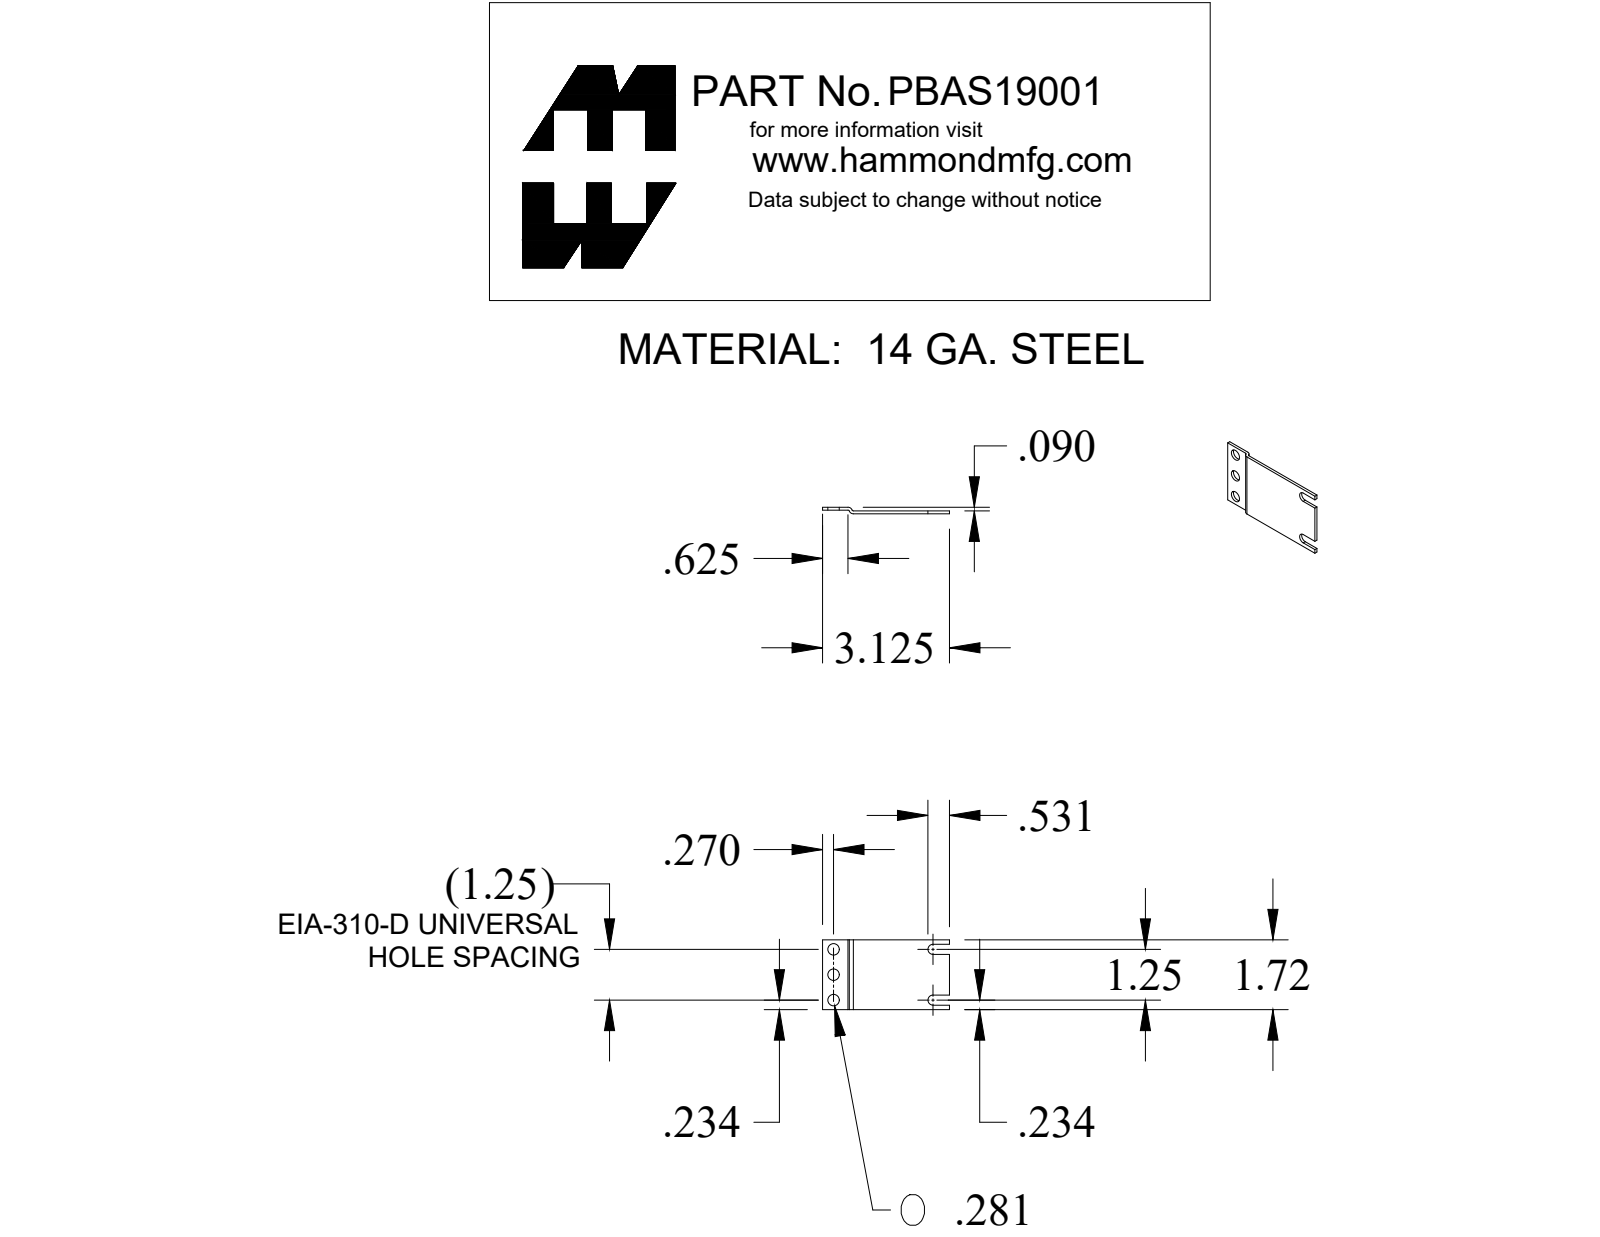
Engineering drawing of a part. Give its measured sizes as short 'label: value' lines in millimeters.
name: PBAS19001BK2
written by: SolidWorks 2019 (CONFIG_CONTROL_DESIGN)
unit: mm
bodies: 1 solid, 23 faces (14 planar, 9 cylindrical, 0 other)
size: 79.4 × 43.6 × 4.1
volume: 5 900 mm³; area: 7 110 mm²
holes: 3× ⌀7.1
rounds: 2× R0.9, 2× R2.7, 2× R3.2
face distances: 1.8, 2.3, 4.1, 0.5, 2.3, 1.8, 43.6, 79.4, 2.8, 40.9
hole spacings: 15.9, 31.8
